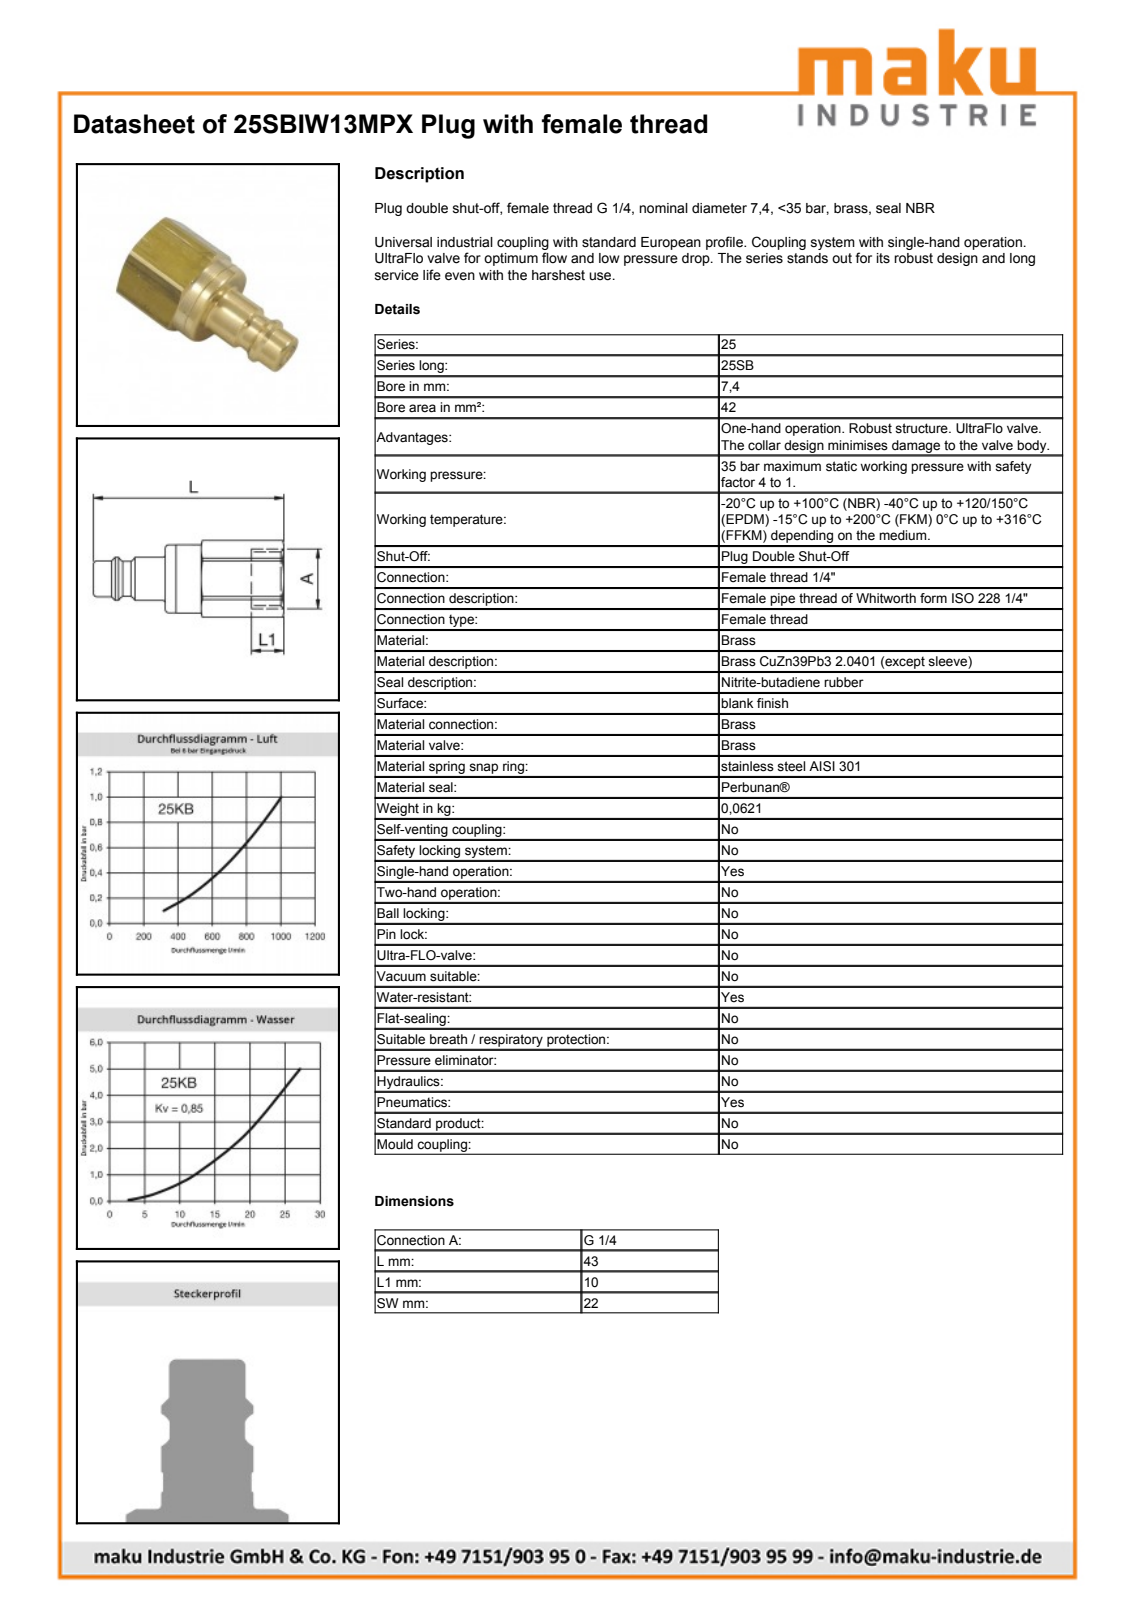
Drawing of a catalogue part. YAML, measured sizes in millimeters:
part_name: "D111025"
step_written_by: "Autodesk Inventor 2013 (AUTOMOTIVE_DESIGN)"
units: millimeters
bodies: {solids: 1, faces: 58, planar: 17, cylindrical: 17, other: 24}
overall_size: [43.1, 24.68, 23.4]
volume: 7671
surface_area: 4219
round_holes:
  - {diameter: 14.45, count: 1}
  - {diameter: 17, count: 1}
round_bosses_or_shafts:
  - {diameter: 21, count: 1}
  - {diameter: 16.5, count: 1}
  - {diameter: 13.16, count: 1}
  - {diameter: 12, count: 1}
  - {diameter: 10, count: 1}
  - {diameter: 9.75, count: 1}
  - {diameter: 9.66, count: 1}
partial_cylinders:
  - {radius: 12.4, count: 1}
face_to_face_distances: [22, 9, 14.1, 11.1, 4.5, 23.1, 12, 2.1, 7.5, 6.6]
